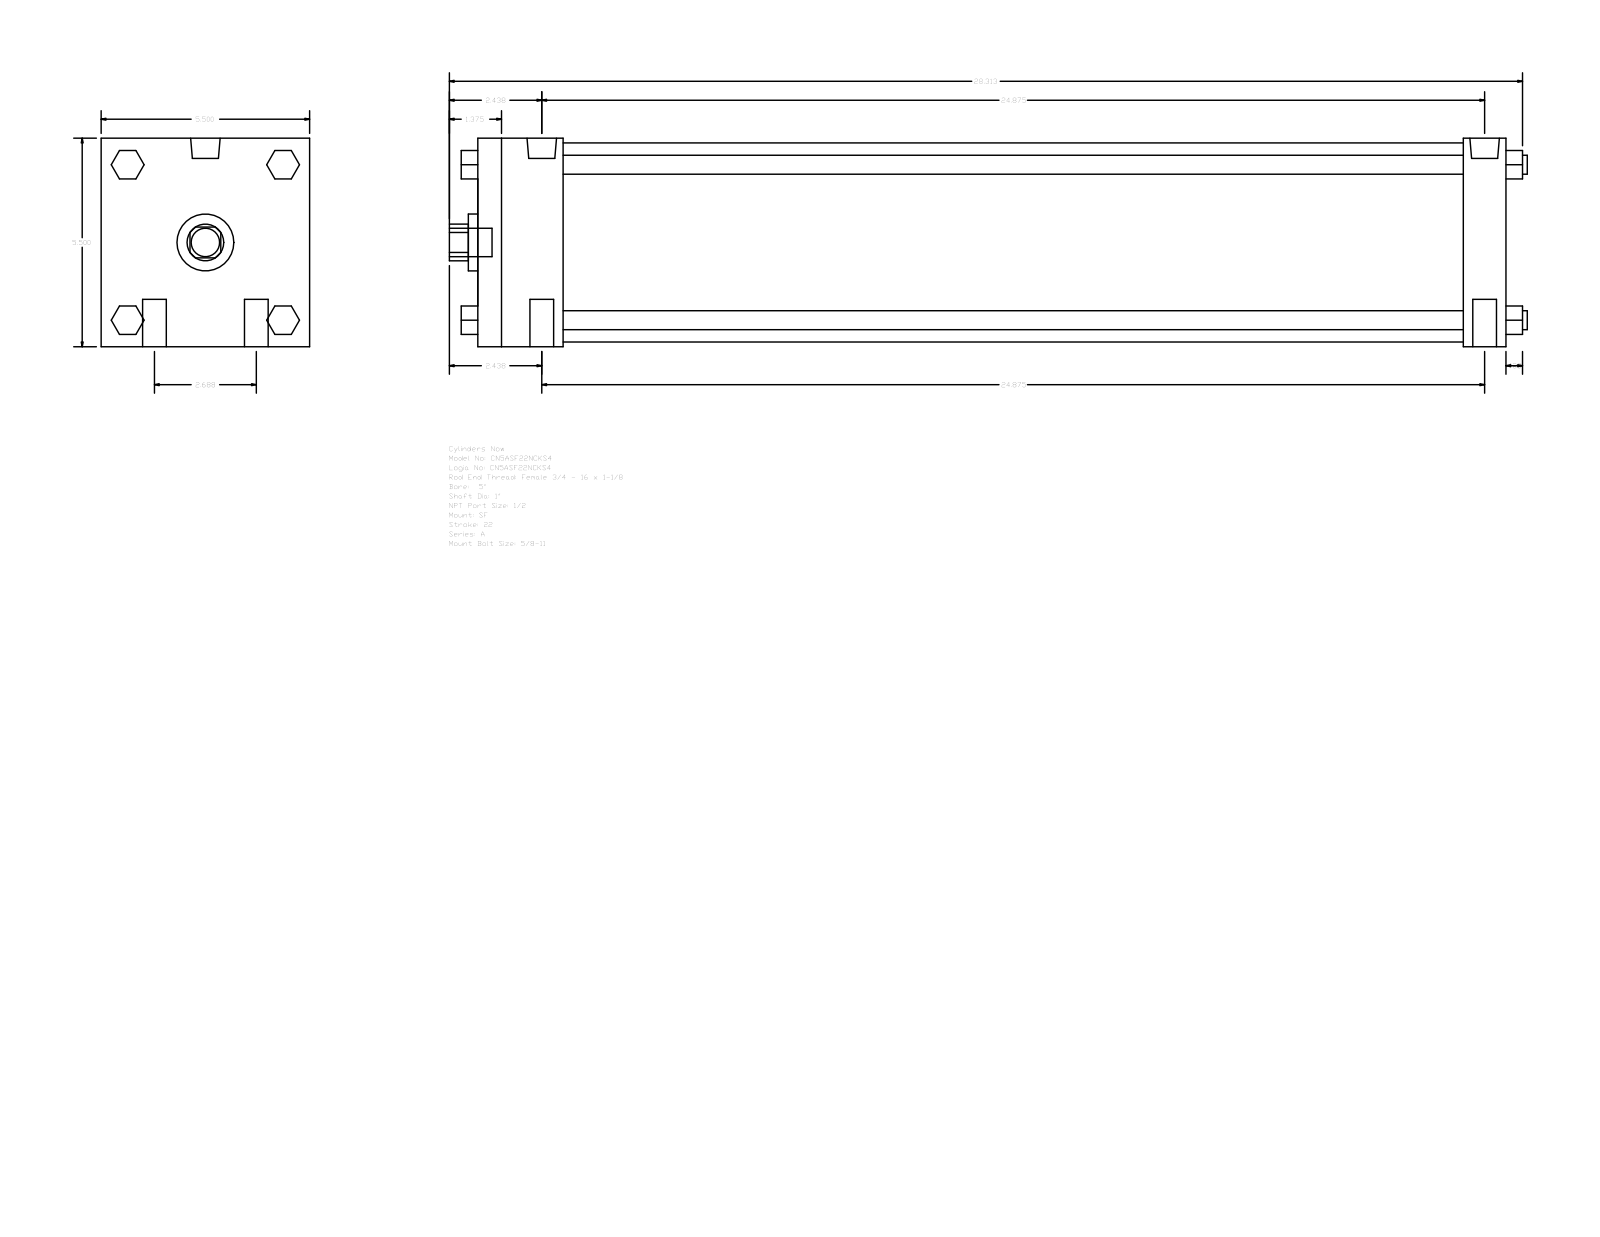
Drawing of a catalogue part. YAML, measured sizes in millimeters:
part_name: "A_SF__0500_1"
step_written_by: "GSSL Pune (CONFIG_CONTROL_DESIGN)"
units: millimeters
bodies: {solids: 0, faces: 124, planar: 94, cylindrical: 30, other: 0}
overall_size: [722.31, 139.7, 139.7]
round_holes:
  - {diameter: 25.4, count: 1}
  - {diameter: 38.1, count: 1}
  - {diameter: 133.35, count: 1}
round_bosses_or_shafts:
  - {diameter: 15.88, count: 4}
  - {diameter: 12.7, count: 4}
  - {diameter: 19.77, count: 2}
  - {diameter: 8.73, count: 2}
  - {diameter: 19.05, count: 1}
partial_cylinders:
  - {radius: 12.29, count: 1}
face_to_face_distances: [139.7, 688.97, 28.57, 57.15, 660.4, 603.25, 631.82, 19.05, 52.07, 90.18]
